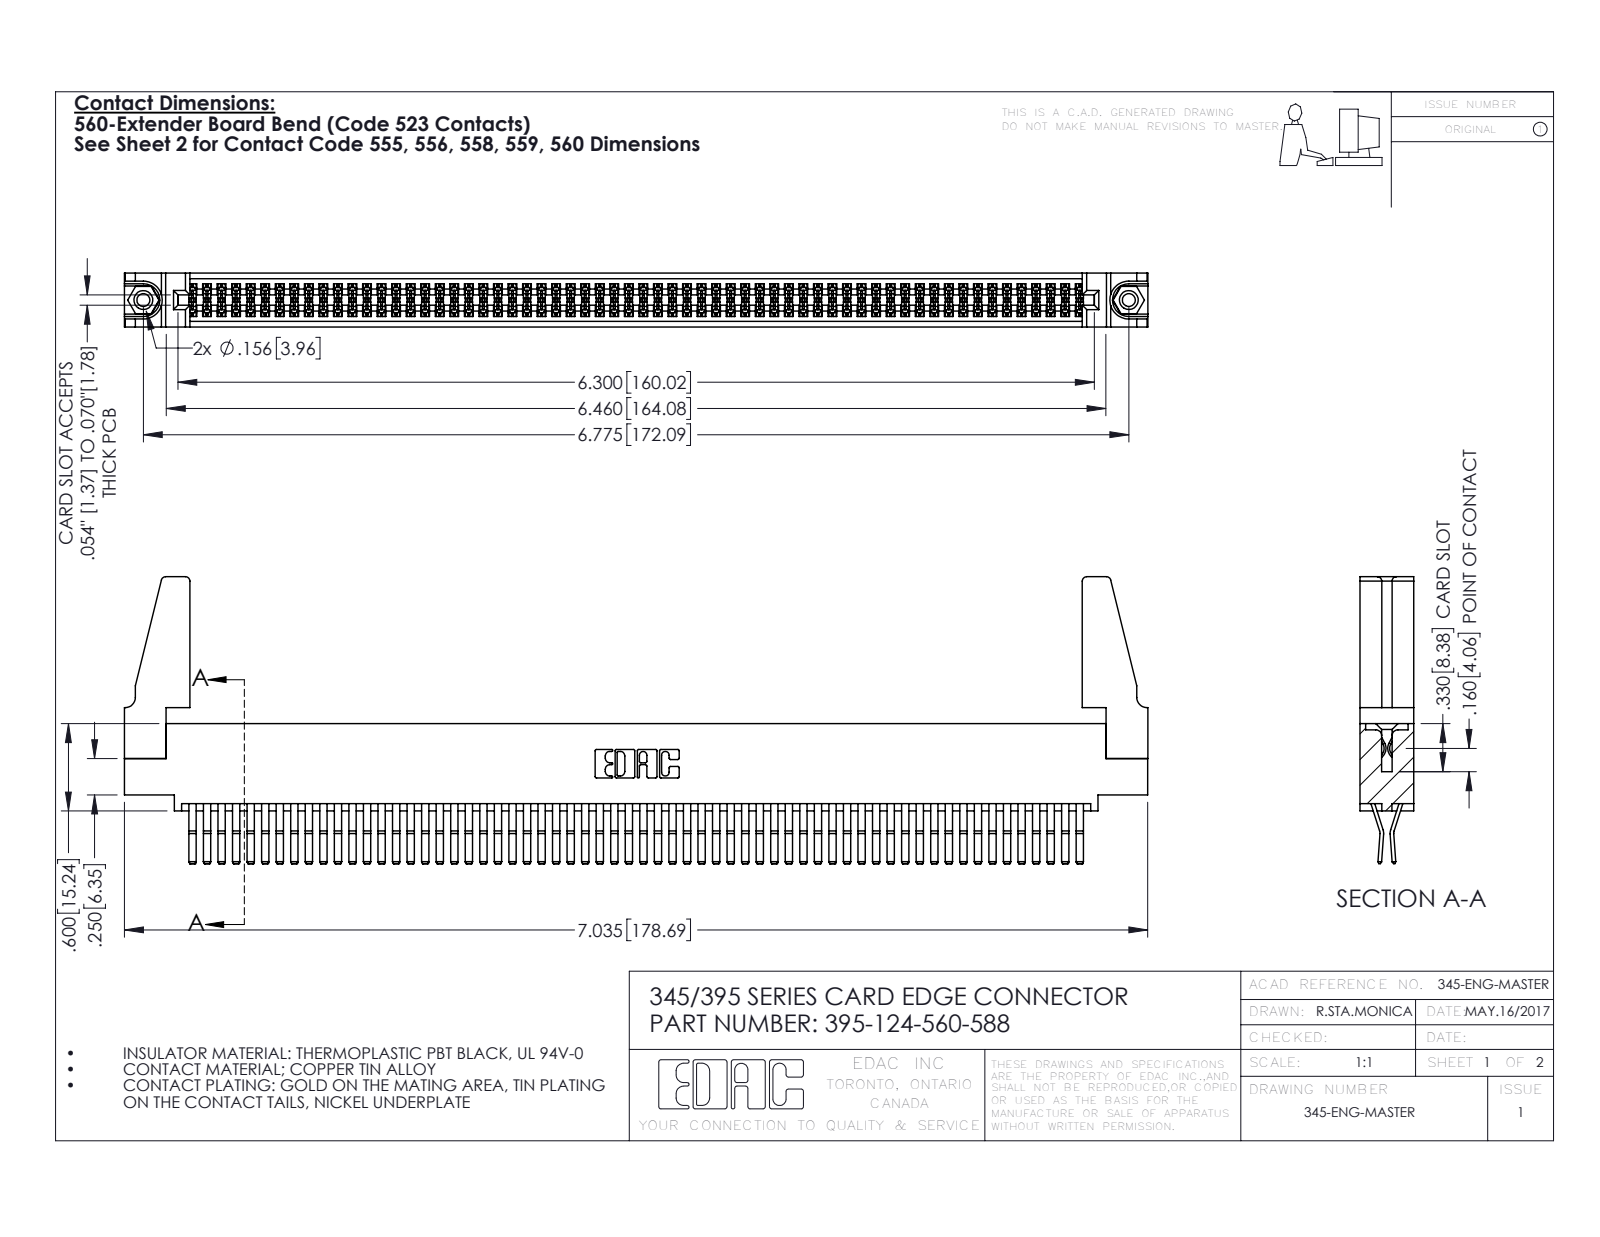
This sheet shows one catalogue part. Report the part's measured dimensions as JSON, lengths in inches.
{"part_name": "345-250-001_345-250-001-102; 345-292-001_560 Tail; 345 Part_0.110 Offset - 0.156 Dia-TH; 345-220-078_345-220-088 (+1 more)", "step_written_by": "SolidWorks 2016 (CONFIG_CONTROL_DESIGN)", "units": "inches", "bodies": {"solids": 129, "faces": 6702, "planar": 4248, "cylindrical": 2438, "other": 16}, "overall_size": [7.036, 1.972, 0.37], "volume_in3": 1.314, "surface_area_in2": 50.72, "round_holes": [[0.089, 2], [0.125, 2], [0.156, 2], [0.064, 1]], "round_bosses_or_shafts": [[0.155, 2]], "partial_cylinders_radius": [[0.006, 187], [0.01, 22], [0.03, 8], [0.007, 6], [0.031, 6], [0.026, 3], [0.01, 2], [0.014, 2]], "face_to_face_distances": [0.072, 0.298, 0.025, 0.37, 0.2, 0.098, 0.272, 0.225, 0.175, 0.149], "hole_center_spacings": [0.27, 6.539, 6.775]}
